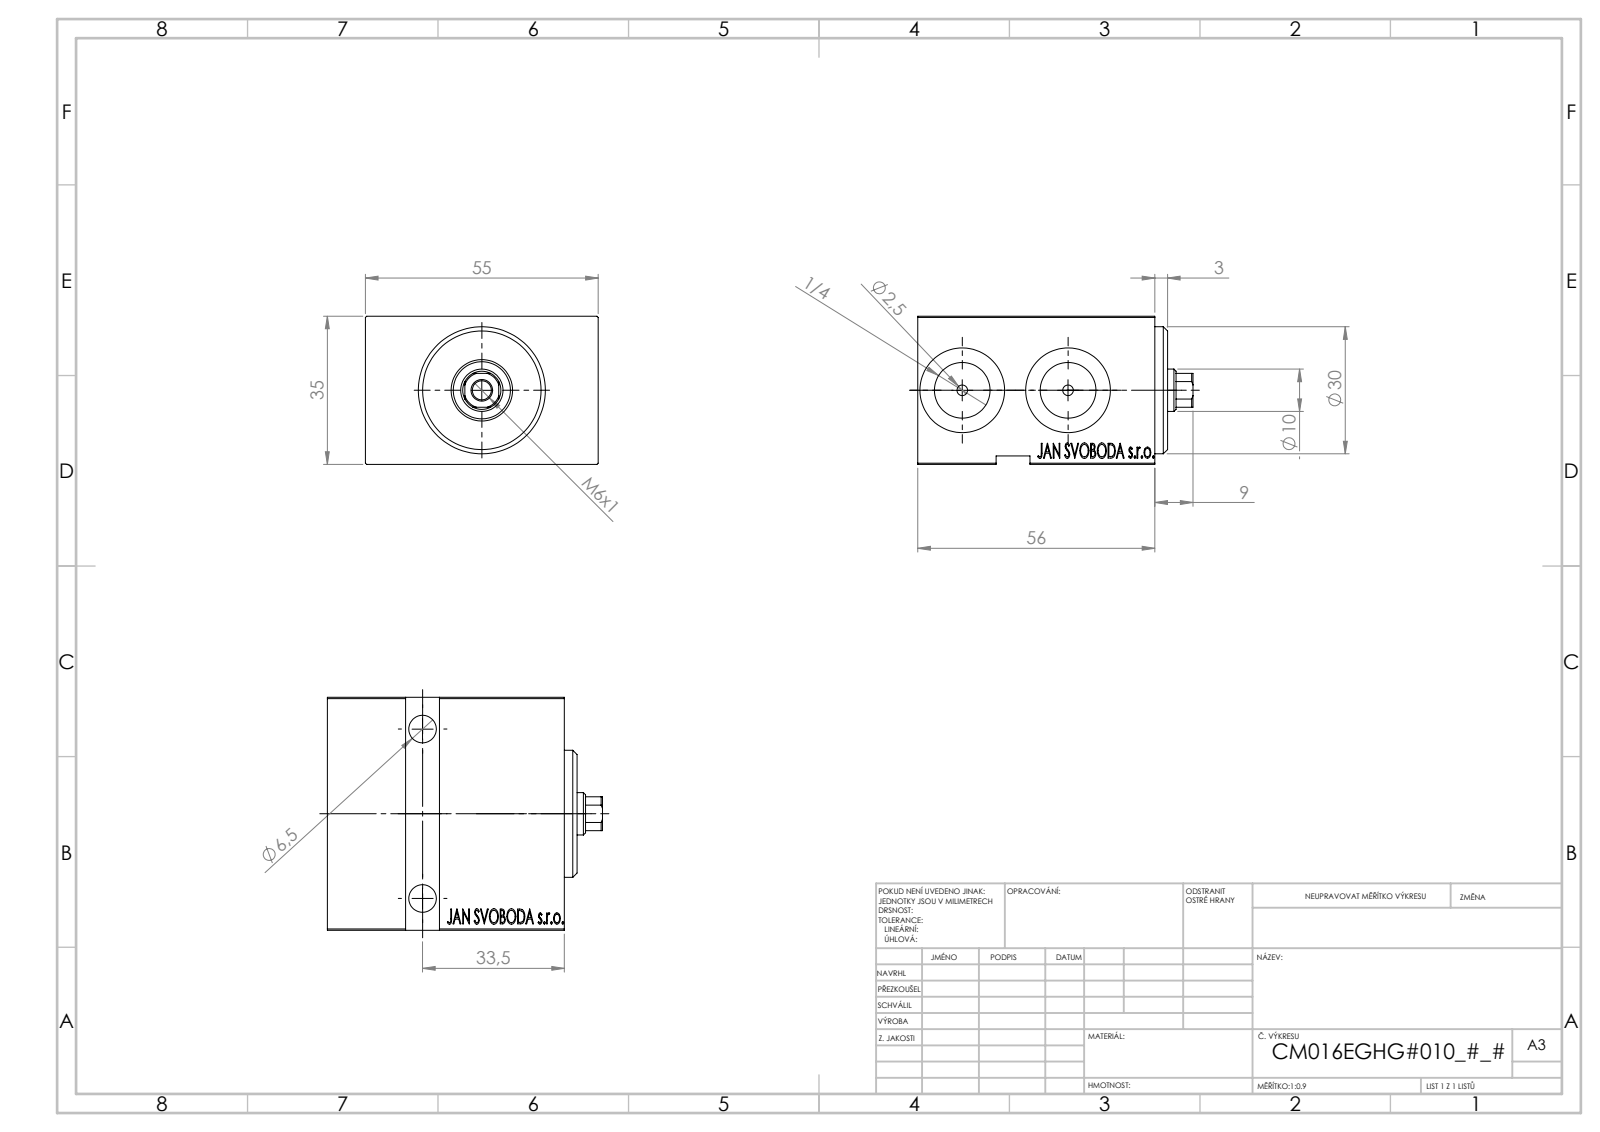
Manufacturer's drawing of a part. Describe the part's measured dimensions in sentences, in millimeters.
The part is named "V450CM_E_VCP; V450CM_VC_B; V450CM_E_Body". Its 3-D file was written by "SolidWorks 2019 (CONFIG_CONTROL_DESIGN)". It is 3 solids with 852 faces: 410 planar, 48 cylindrical and 394 other. Overall it measures 65 by 55 by 35 millimeters. Its volume is 99 960 cubic millimeters and its surface area 25 575 square millimeters. Round holes: 2 of diameter 2.5, 2 of diameter 6.5, 2 of diameter 10.5, 2 of diameter 13.16, 2 of diameter 20, 1 of diameter 4.5, 1 of diameter 10, 1 of diameter 13.5, 1 of diameter 14.5, 1 of diameter 16, 1 of diameter 18, 1 of diameter 25. Round bosses or shafts: 1 of diameter 30. Partial cylindrical surfaces (rounded edges, fillets, slot ends): 1 of radius 4.5. The main face-to-face distances are 35, 56, 55, 5, 51, 8, 3, 59, 46, 54. The hole center spacings are 25, 40.
